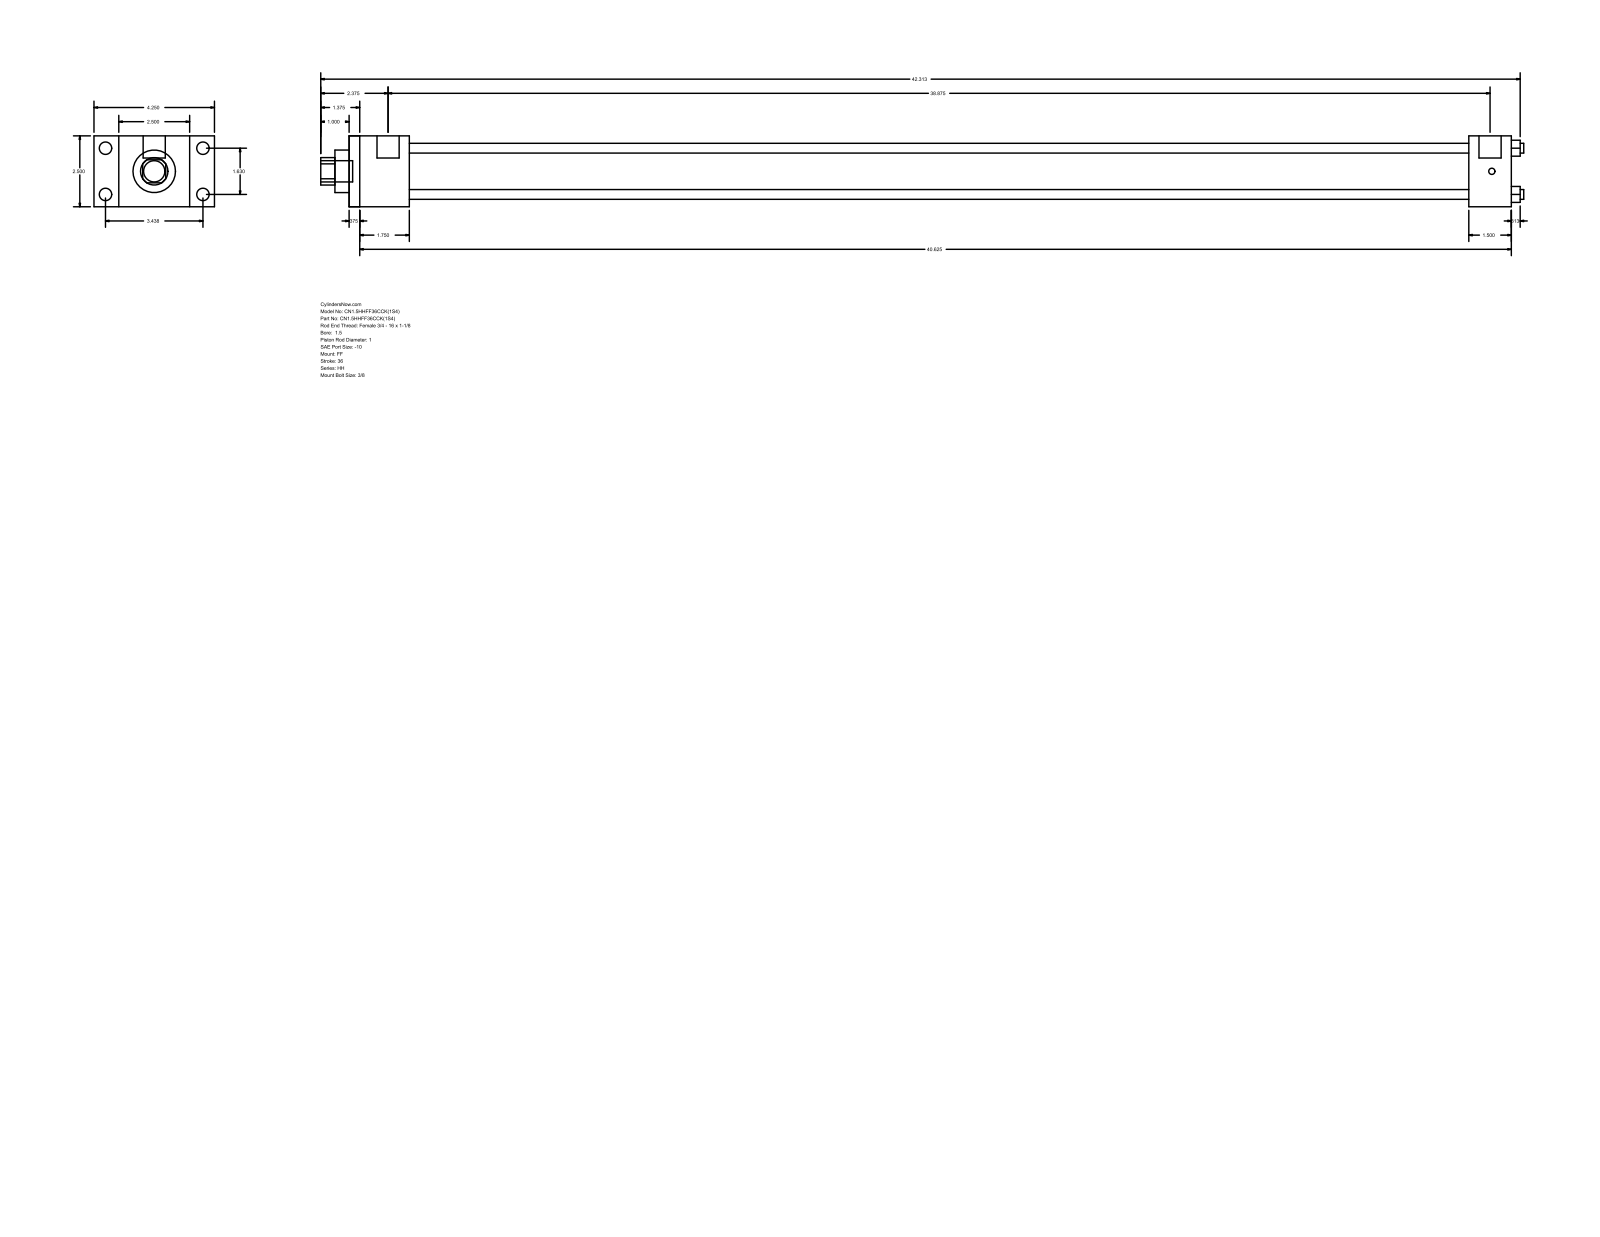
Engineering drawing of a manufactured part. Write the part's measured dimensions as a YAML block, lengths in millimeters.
part_name: "HH_FF__0150_1"
step_written_by: "GSSL Pune (CONFIG_CONTROL_DESIGN)"
units: millimeters
bodies: {solids: 0, faces: 92, planar: 64, cylindrical: 28, other: 0}
overall_size: [1077.91, 107.95, 63.5]
round_holes:
  - {diameter: 8.76, count: 4}
  - {diameter: 25.4, count: 1}
  - {diameter: 38.1, count: 1}
  - {diameter: 44.45, count: 1}
round_bosses_or_shafts:
  - {diameter: 11.13, count: 4}
  - {diameter: 5.56, count: 4}
  - {diameter: 19.84, count: 2}
  - {diameter: 19.05, count: 1}
partial_cylinders:
  - {radius: 12.29, count: 1}
face_to_face_distances: [63.5, 1041.4, 9.52, 1031.88, 53.98, 44.46, 987.42, 1003.3, 993.78, 949.32]
hole_center_spacings: [29.27, 41.4, 58.55]
